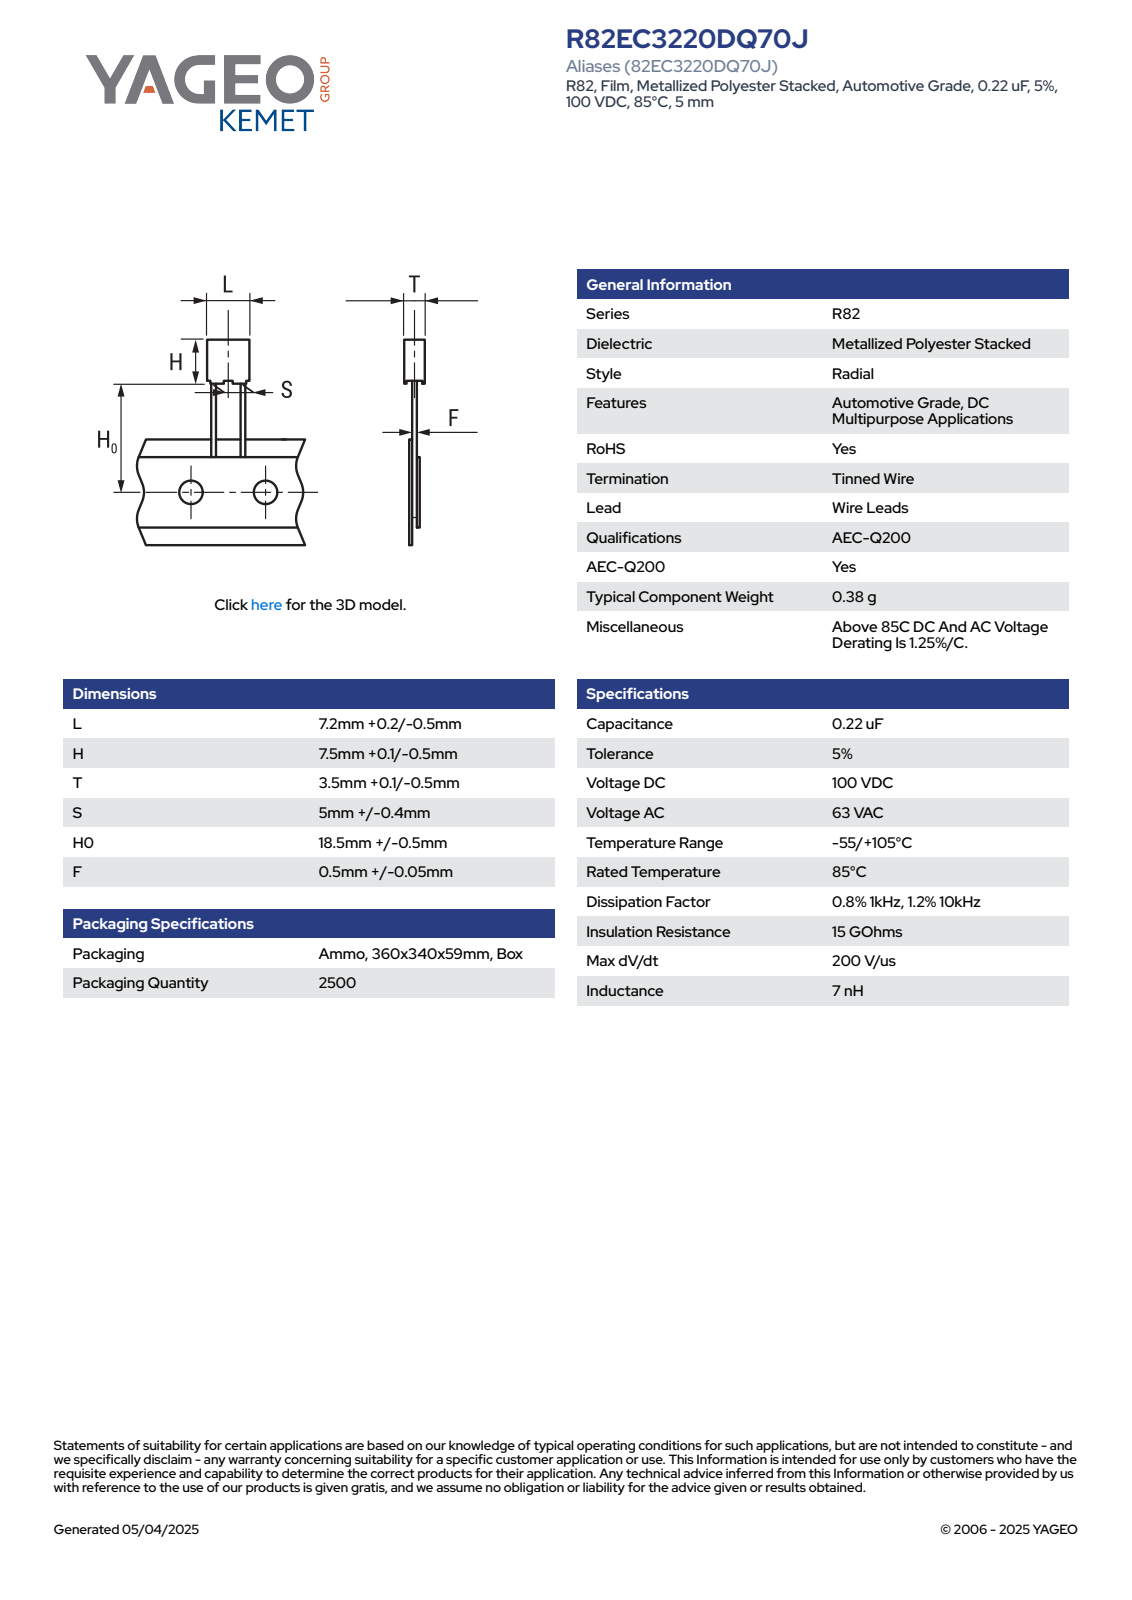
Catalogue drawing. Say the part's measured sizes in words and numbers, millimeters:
The part is named "CFR_RB3_7.2X7.5X3.5_L7.4H7.6T3.6S5H019F0.55". Its 3-D file was written by "SolidWorks 2014 (AUTOMOTIVE_DESIGN)". It is 4 solids with 85 faces: 77 planar, 8 cylindrical and 0 other. Overall it measures 26.6 by 7.4 by 3.6 millimeters. Its volume is 194 cubic millimeters and its surface area 301 square millimeters. Round bosses or shafts: 2 of diameter 0.55. Partial cylindrical surfaces (rounded edges, fillets, slot ends): 4 of radius 0.5. The main face-to-face distances are 3.6, 7.4, 6.85, 3.35, 3.1, 7.15, 0.75, 7.6, 6.9, 0.49.
